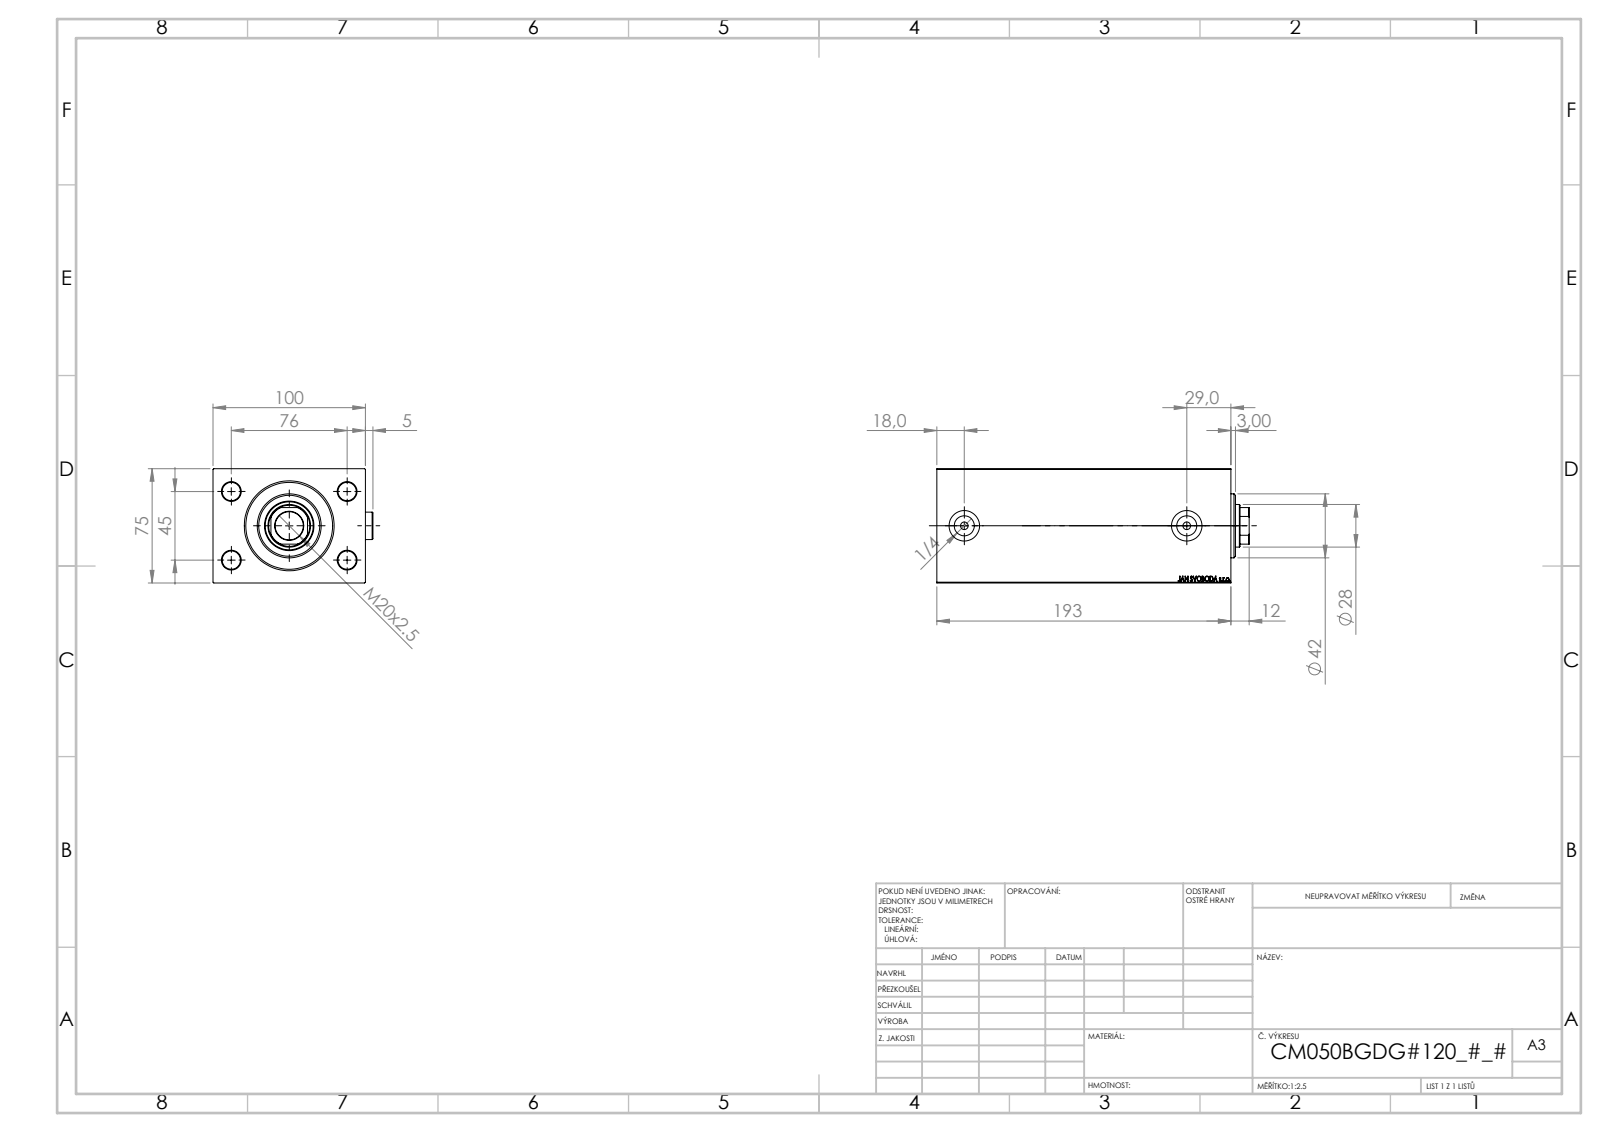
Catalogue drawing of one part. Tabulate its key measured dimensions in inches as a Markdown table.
| quantity | value |
| --- | --- |
| part name | V450CM_B_Body; V450CM_VC_B; V450CM_B_VCP; Zatka_OIL_PORT |
| STEP written by | SolidWorks 2019 (CONFIG_CONTROL_DESIGN) |
| units | inches |
| bodies | 5 solids, 938 faces (436 planar, 72 cylindrical, 430 other) |
| overall size | 8.071 × 4.13 × 2.953 |
| volume | 77.01 in³ |
| surface area | 238.9 in² |
| round holes (diameter × count) | 0.472 × 4, 0.197 × 2, 0.518 × 2, 0.787 × 2, 0.728 × 1, 1.102 × 1, 1.24 × 1, 1.28 × 1, 1.969 × 1, 2.047 × 1, 2.244 × 1 |
| round bosses / shafts (diameter × count) | 0.709 × 2, 1.654 × 1 |
| partial cylindrical surfaces (radius × count) | 0.531 × 1 |
| main face-to-face distances | 2.953, 3.937, 7.598, 0.551, 7.047, 0.472, 6.575, 7.126, 2.402, 5.197 |
| hole center spacings | 1.739, 1.772, 2.992, 3.477, 5.748 |
